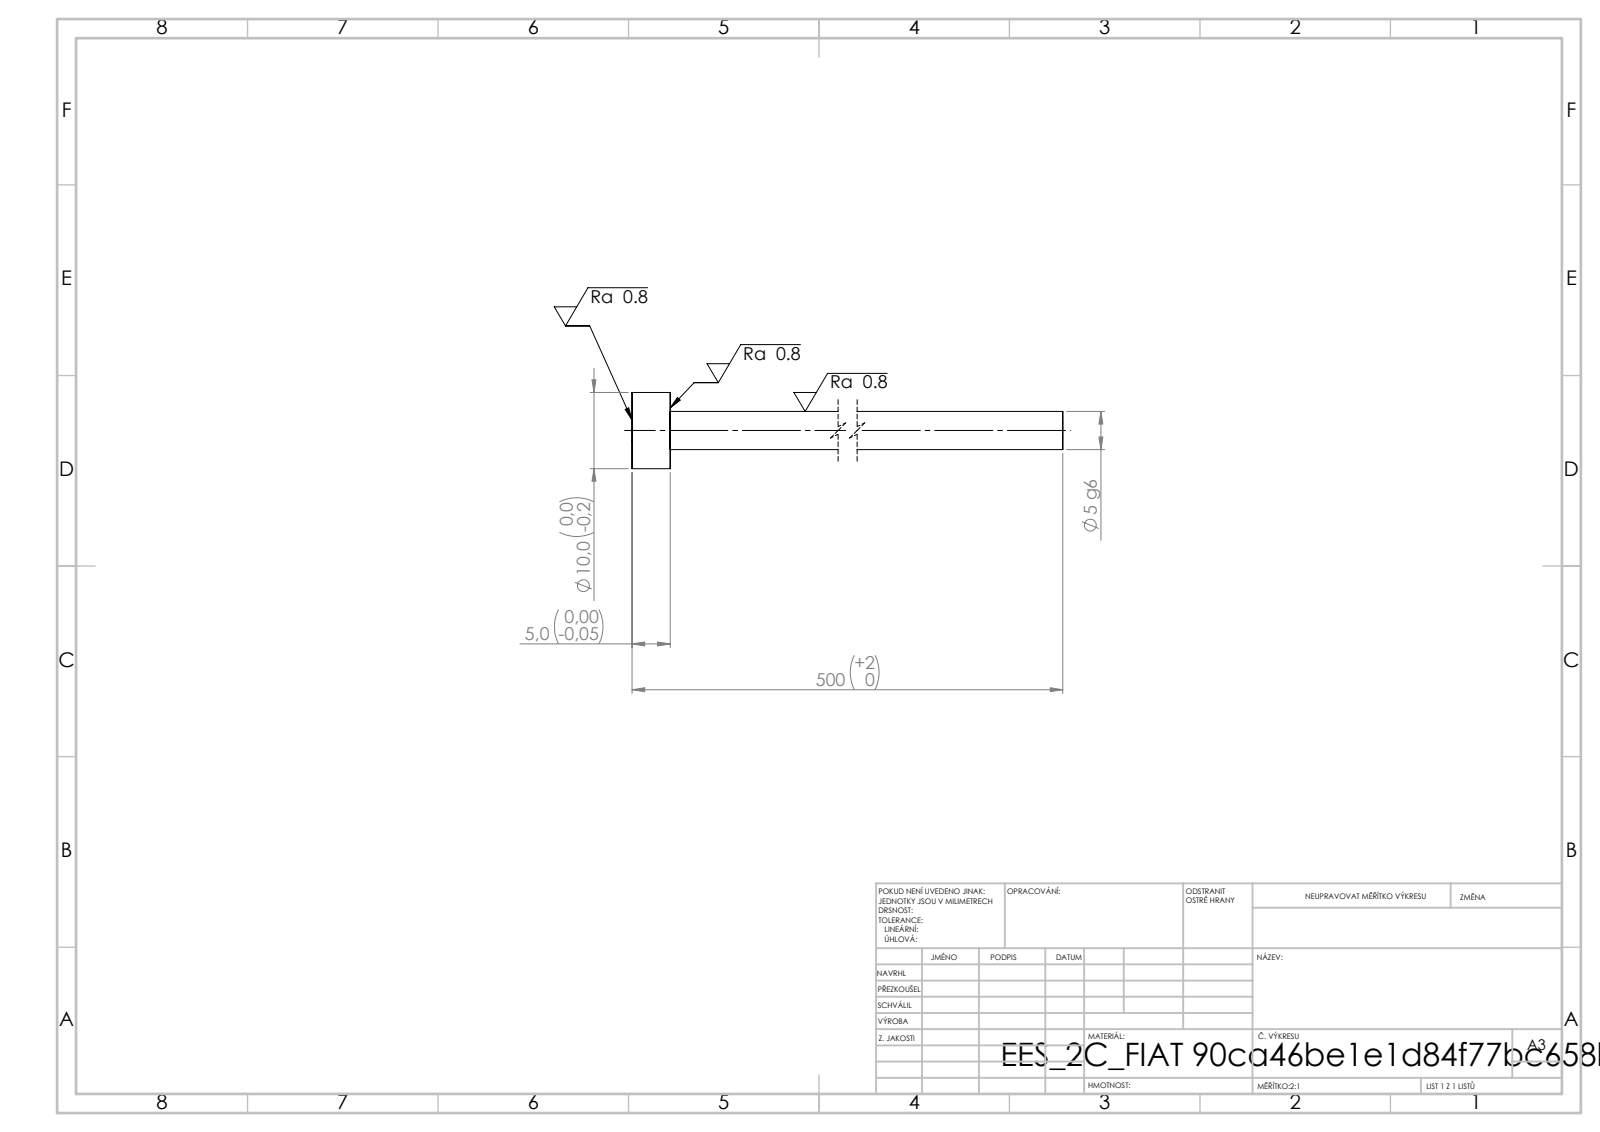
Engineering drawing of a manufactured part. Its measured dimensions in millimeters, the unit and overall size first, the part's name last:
Units: millimetres
Overall size (bounding box): 500 × 10 × 10
Round bosses / shafts (diameter × count): ⌀10 ×1, ⌀5 ×1
Main face-to-face distances: 5, 500, 495
Volume: 10 112 mm³ · Surface area: 8 090 mm²
Bodies: 1 solid, 7 faces (3 planar, 4 cylindrical, 0 other)
STEP written by: SolidWorks 2019 (CONFIG_CONTROL_DESIGN)
